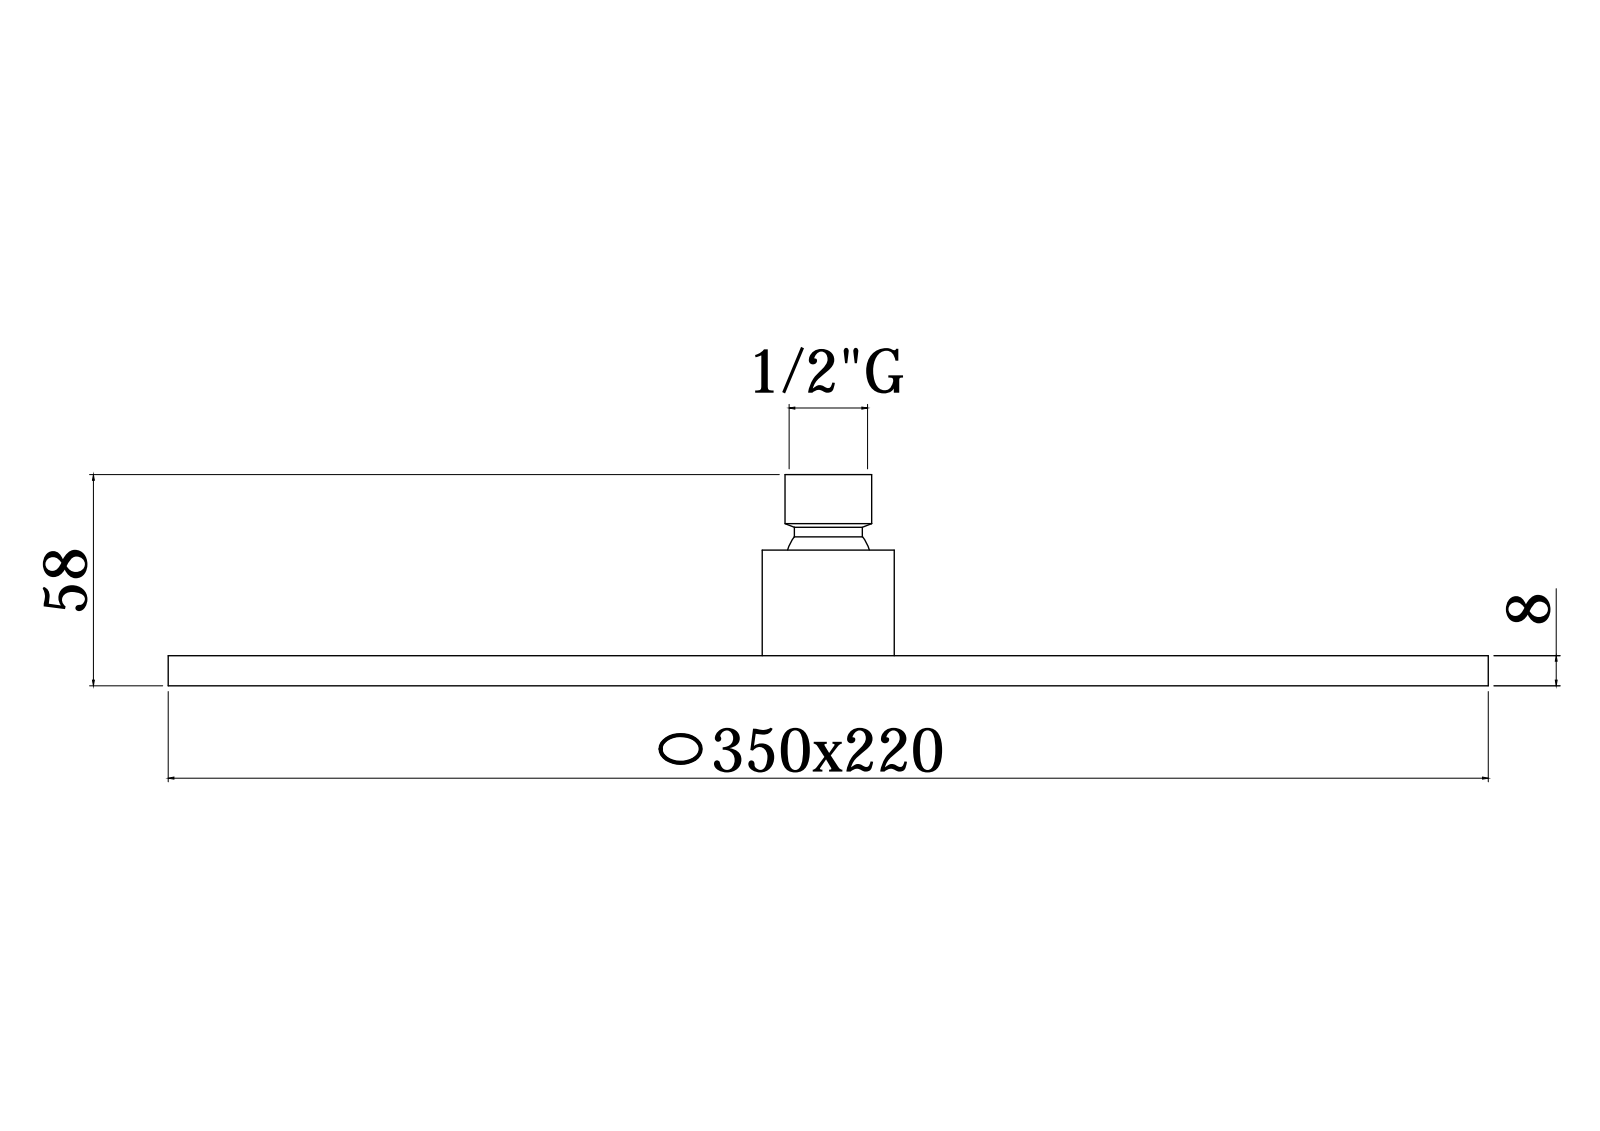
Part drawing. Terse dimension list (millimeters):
name: ZSOF080CR
written by: CREO PARAMETRIC BY PTC INC, 2020044 (CONFIG_CONTROL_DESIGN)
unit: mm
bodies: 1 solid, 4345 faces (546 planar, 1004 cylindrical, 2795 other)
size: 350.49 × 220.49 × 51.9
volume: 281 650 mm³; area: 250 364 mm²
holes: 128× ⌀1.5, 128× ⌀1.7, 17× ⌀7, 16× ⌀2.5, 16× ⌀5.1, 1× ⌀15, 1× ⌀16, 1× ⌀16.5, 1× ⌀18.63, 1× ⌀23.8, 1× ⌀24, 1× ⌀26.5
bosses: 128× ⌀10, 16× ⌀6, 16× ⌀5, 1× ⌀31.8, 1× ⌀29.4, 1× ⌀28, 1× ⌀23.2
rounds: 9× R20
face distances: 8.5, 7.5, 1, 1.5, 6, 7, 5.6, 2.9, 1.4, 4.6
hole spacings: 120, 31.33, 46.82, 140, 15.26, 15.69, 48.6, 52.57
